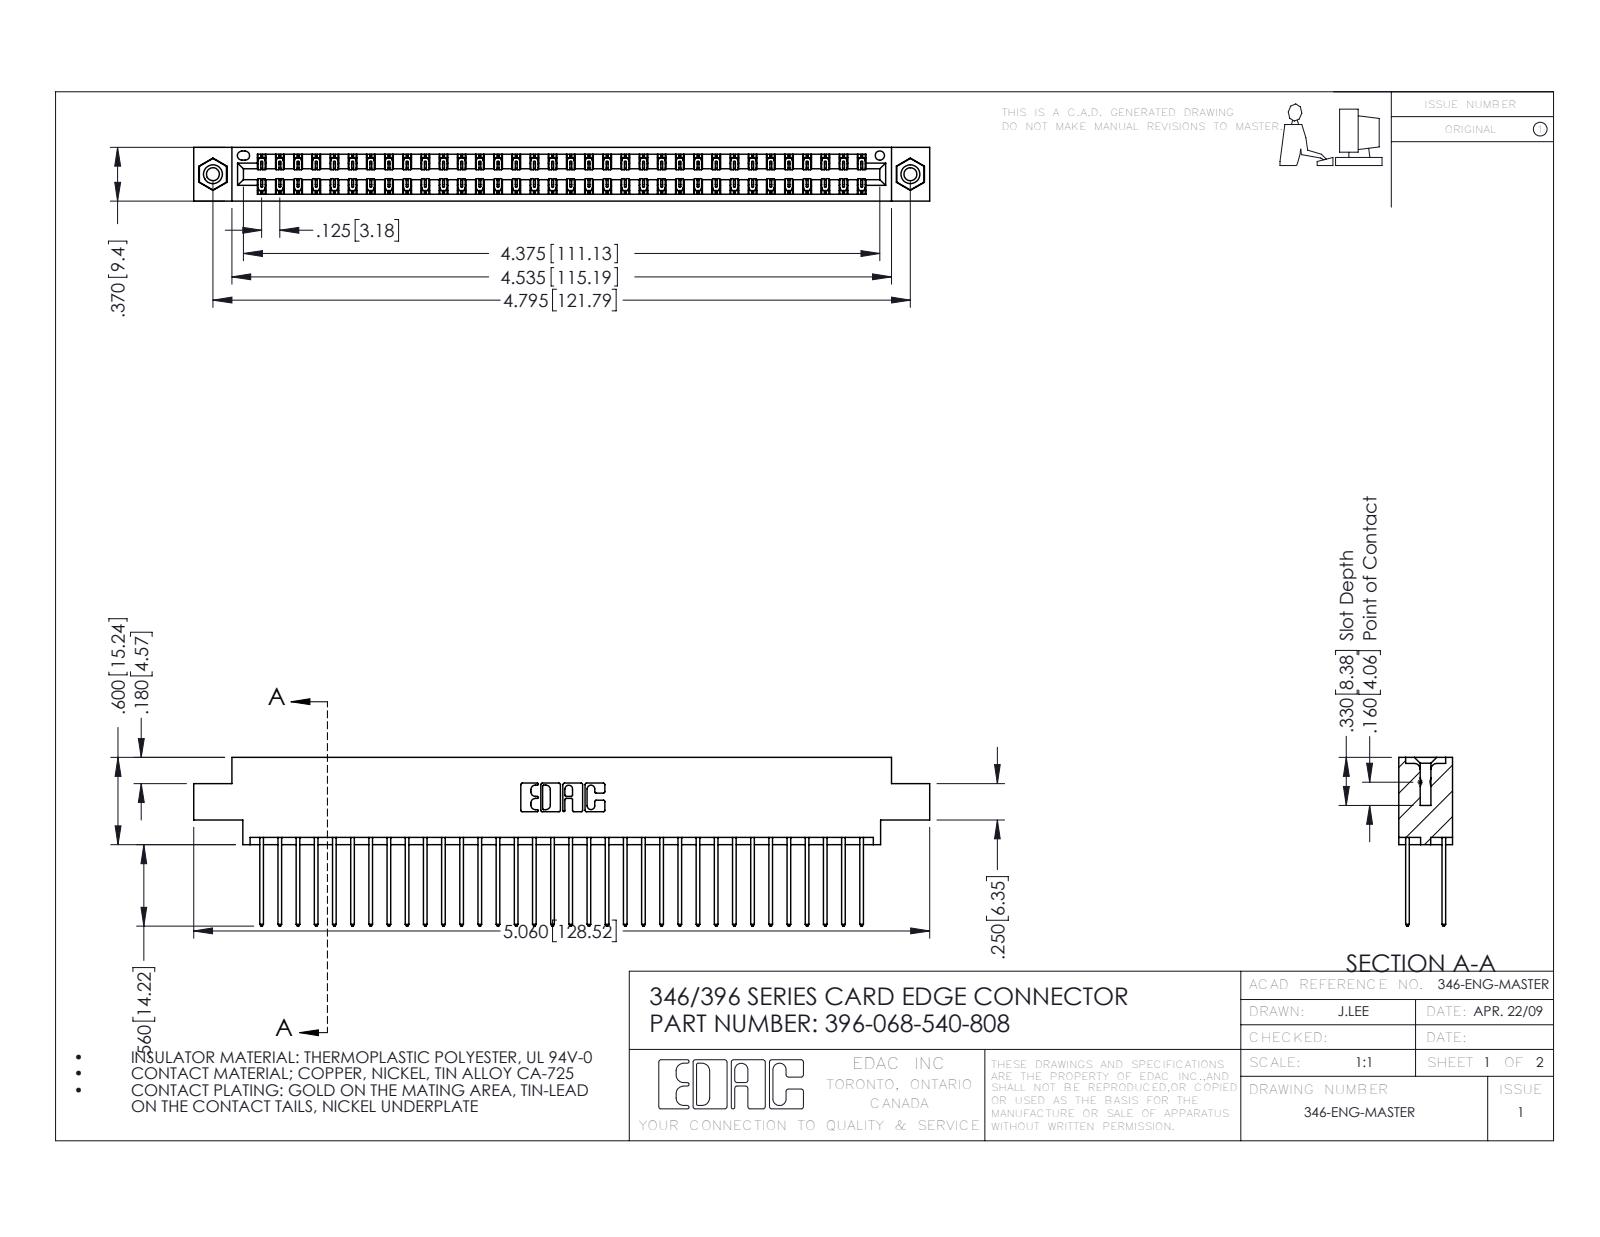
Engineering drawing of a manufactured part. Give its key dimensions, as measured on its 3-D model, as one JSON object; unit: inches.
{"part_name": "346 Part_0.170 Offset - 0.156 Dia-TI; 345-250-001_345-250-003-102; 396-068-540-808; 345-292-001_345-293-140", "step_written_by": "SolidWorks 2016 (CONFIG_CONTROL_DESIGN)", "units": "inches", "bodies": {"solids": 71, "faces": 3722, "planar": 2492, "cylindrical": 1214, "other": 16}, "overall_size": [5.06, 1.16, 0.37], "volume_in3": 0.767, "surface_area_in2": 28.78, "round_holes": [[0.089, 2], [0.125, 2], [0.156, 2], [0.064, 1]], "round_bosses_or_shafts": [[0.155, 2]], "partial_cylinders_radius": [[0.006, 102], [0.01, 68], [0.01, 22], [0.007, 6], [0.031, 6], [0.026, 3], [0.014, 2], [0.022, 2]], "face_to_face_distances": [0.048, 0.322, 0.25, 0.072, 0.298, 0.025, 0.37, 0.275, 0.222, 0.148], "hole_center_spacings": [0.246, 4.587, 4.795]}
